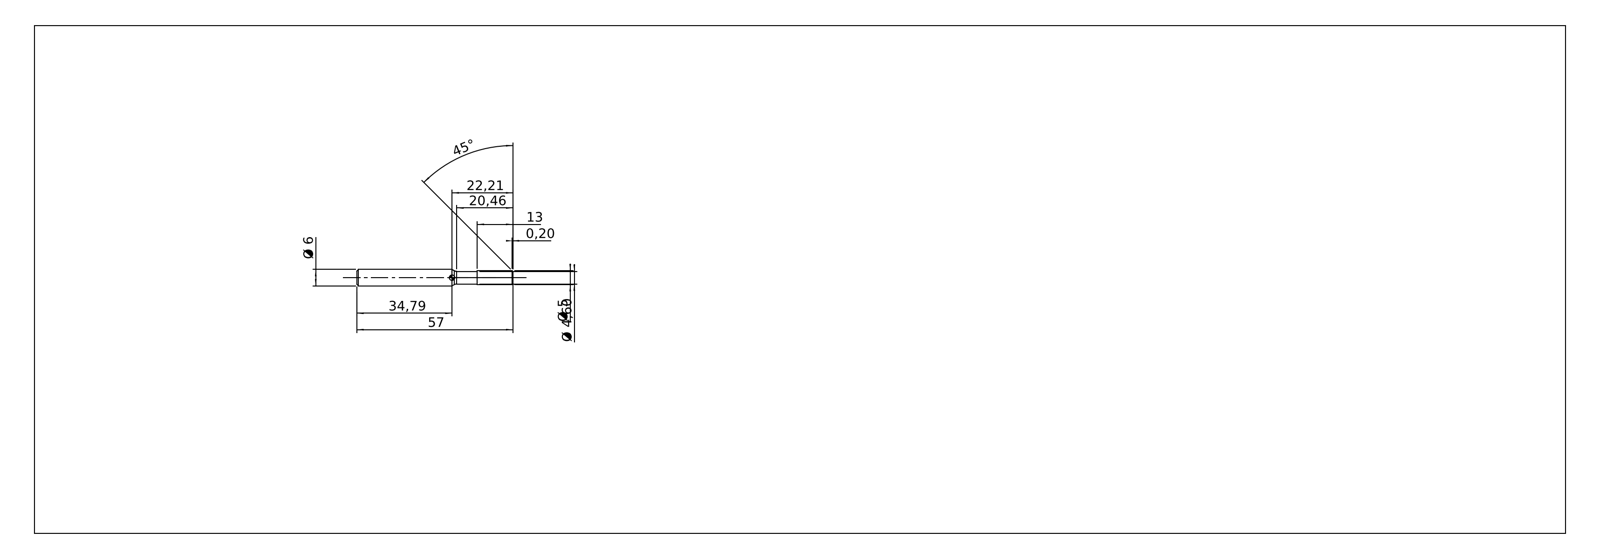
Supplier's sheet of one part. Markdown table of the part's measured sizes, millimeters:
| quantity | value |
| --- | --- |
| part name | 738.050.00 |
| STEP written by | SolidWorks 2019 (CONFIG_CONTROL_DESIGN) |
| units | millimeters |
| bodies | 2 solids, 11 faces (4 planar, 3 cylindrical, 4 other) |
| overall size | 57 × 6 × 6 |
| volume | 1 396 mm³ |
| surface area | 1 074 mm² |
| round bosses / shafts (diameter × count) | 6 × 1, 5 × 1, 4.6 × 1 |
| main face-to-face distances | 44, 13, 57 |
